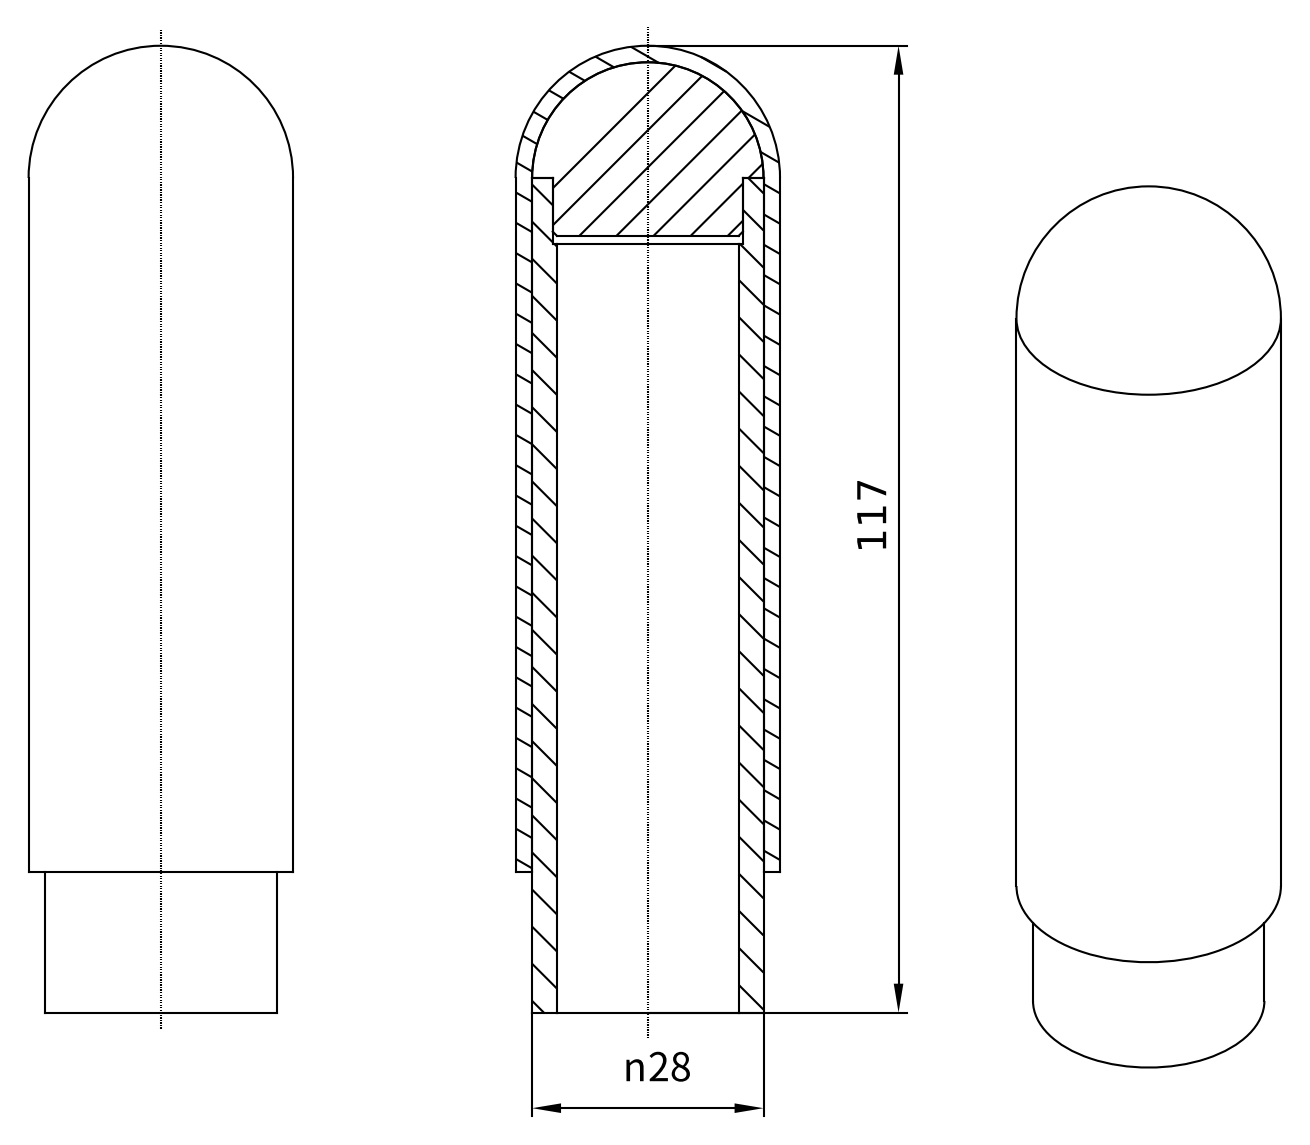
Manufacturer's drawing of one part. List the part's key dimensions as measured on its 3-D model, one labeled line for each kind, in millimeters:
STEP written by: Autodesk Inventor 8 (AUTOMOTIVE_DESIGN)
Units: millimetres
Bodies: 1 solid, 16 faces (4 planar, 8 cylindrical, 4 other)
Overall size (bounding box): 117 × 32 × 32
Volume: 50 827 mm³ · Surface area: 18 974 mm²
Round holes (diameter × count): ⌀22 ×1, ⌀23 ×1
Round bosses / shafts (diameter × count): ⌀32 ×1, ⌀28 ×1
Main face-to-face distances: 94, 17, 77, 93, 76, 1
